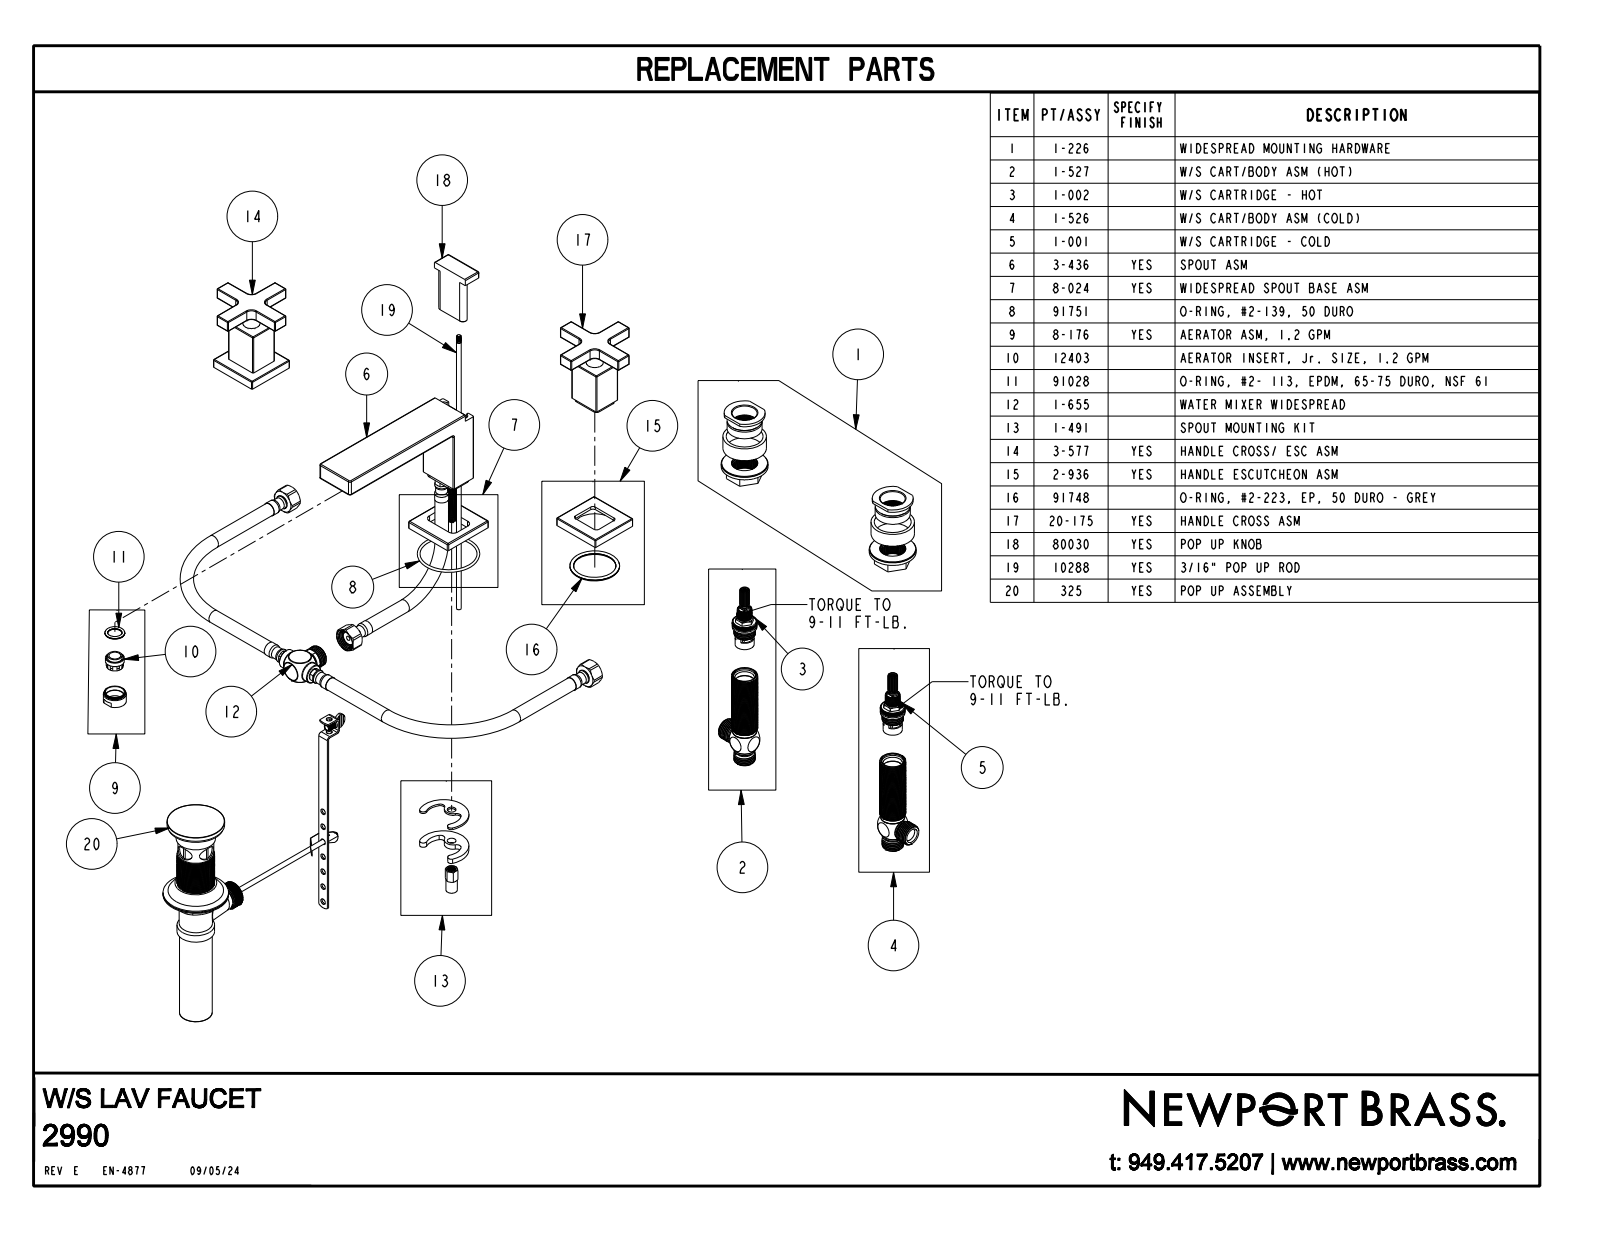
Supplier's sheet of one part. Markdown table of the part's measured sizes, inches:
| quantity | value |
| --- | --- |
| part name | MSBR-3_1; MSBR-2; MSBR-1; 2990_ASM |
| STEP written by | CREO PARAMETRIC BY PTC INC, 2018400 (CONFIG_CONTROL_DESIGN) |
| units | inches |
| bodies | 3 solids, 296 faces (76 planar, 140 cylindrical, 80 other) |
| overall size | 11.14 × 7.717 × 3.46 |
| volume | 25.26 in³ |
| surface area | 122 in² |
| round bosses / shafts (diameter × count) | 0.65 × 2, 0.523 × 2, 0.875 × 1 |
| partial cylindrical surfaces (radius × count) | 0.03 × 68, 0.04 × 21, 0.25 × 8, 0.08 × 3 |
| main face-to-face distances | 3.46, 2.806, 0.654, 0.037, 1.123, 0.24, 8, 1.67, 3.046, 0.414 |
